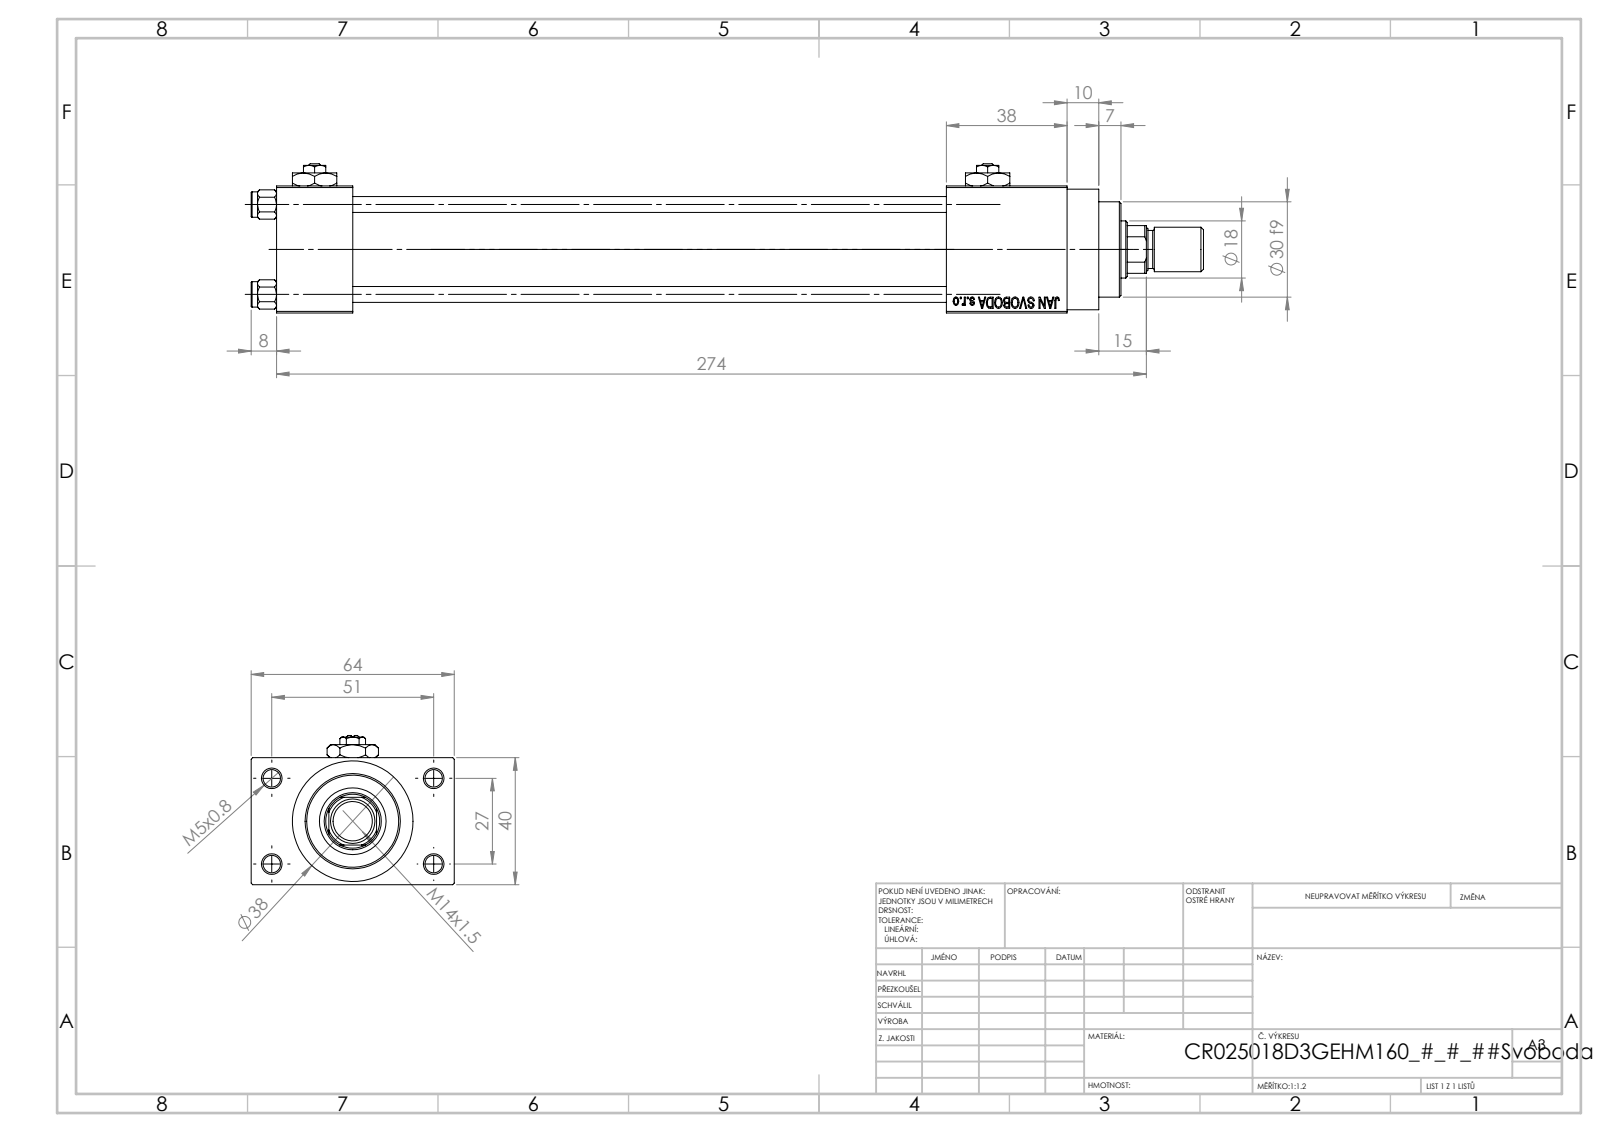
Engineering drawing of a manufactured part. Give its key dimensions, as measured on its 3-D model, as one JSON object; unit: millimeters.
{"part_name": "Zatka_pro_OIL_PORT; NUT_M5_D; ROD_END_AH; V215_VC_A (+3 more)", "step_written_by": "SolidWorks 2019 (CONFIG_CONTROL_DESIGN)", "units": "millimeters", "bodies": {"solids": 14, "faces": 1213, "planar": 545, "cylindrical": 102, "other": 566}, "overall_size": [300, 64, 47], "volume_mm3": 266001, "surface_area_mm2": 108334, "round_holes": [[5, 4], [5.5, 4], [20, 3], [7, 2], [13.16, 2], [8.5, 1], [18, 1], [21, 1], [25, 1], [30, 1]], "round_bosses_or_shafts": [[8, 4], [38, 1], [31, 1], [14, 1], [12, 1]], "partial_cylinders_radius": [[8.5, 1]], "face_to_face_distances": [40, 12, 52, 187, 24, 211, 64, 38, 225, 249], "hole_center_spacings": [11.37, 20.01, 28.3, 28.85, 29.89, 39.66, 48.34, 27]}
